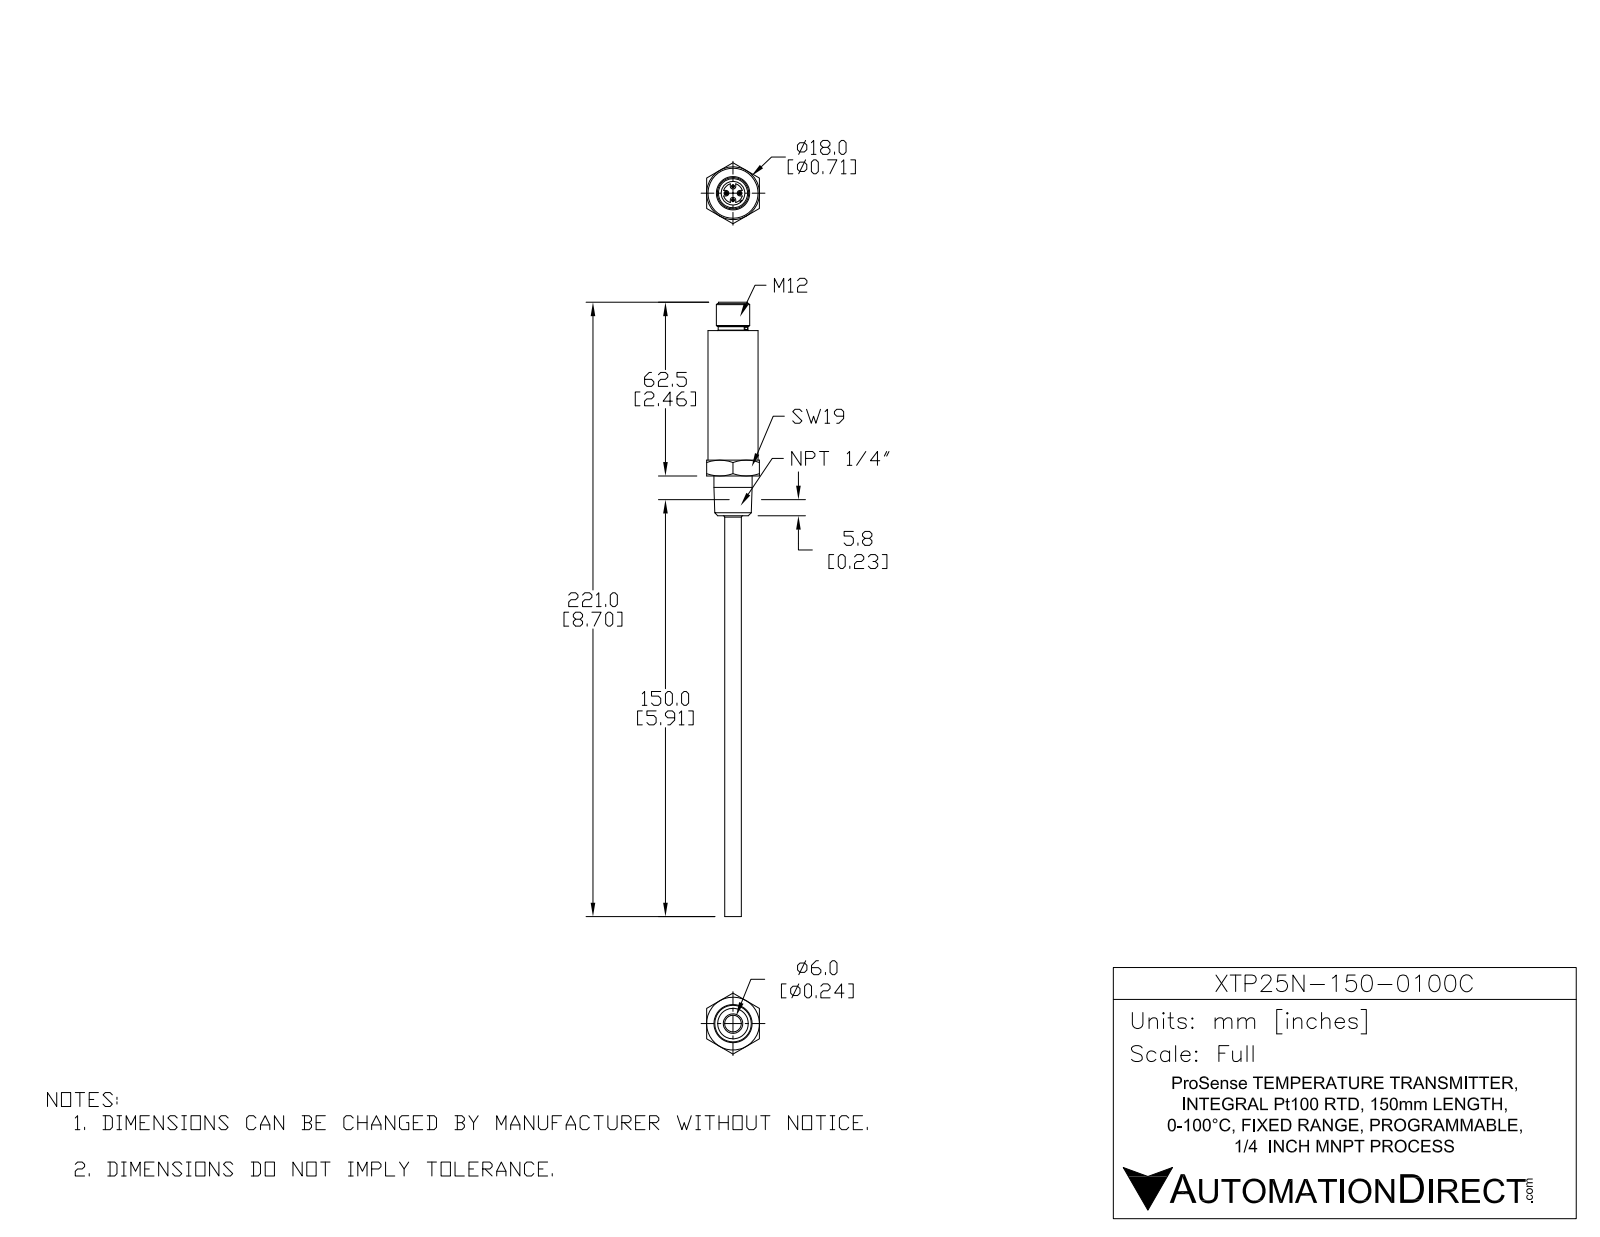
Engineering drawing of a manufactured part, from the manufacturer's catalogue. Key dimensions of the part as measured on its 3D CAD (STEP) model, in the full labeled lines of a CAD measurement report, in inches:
Part name (STEP PRODUCT): XTP25N-150-0100C
STEP written by: SolidWorks 2015 (AUTOMOTIVE_DESIGN)
Units: inches
Bodies: 1 solid, 117 faces (43 planar, 34 cylindrical, 40 other)
Overall size (bounding box): 8.701 × 0.864 × 0.748
Volume: 1.224 in³ · Surface area: 12.23 in²
Round holes (diameter × count): ⌀0.157 ×1, ⌀0.335 ×1
Round bosses / shafts (diameter × count): ⌀0.04 ×4, ⌀0.709 ×1, ⌀0.54 ×1, ⌀0.472 ×1, ⌀0.421 ×1, ⌀0.413 ×1, ⌀0.236 ×1
Partial cylindrical surfaces — rounded edges, fillets, slot ends (radius × count): R0.039 ×4, R0.138 ×1, R0.167 ×1
Main face-to-face distances: 0.748, 2.059, 0.563, 2.622, 0.787, 0.224, 1.835, 3.024, 2.461, 2.236
